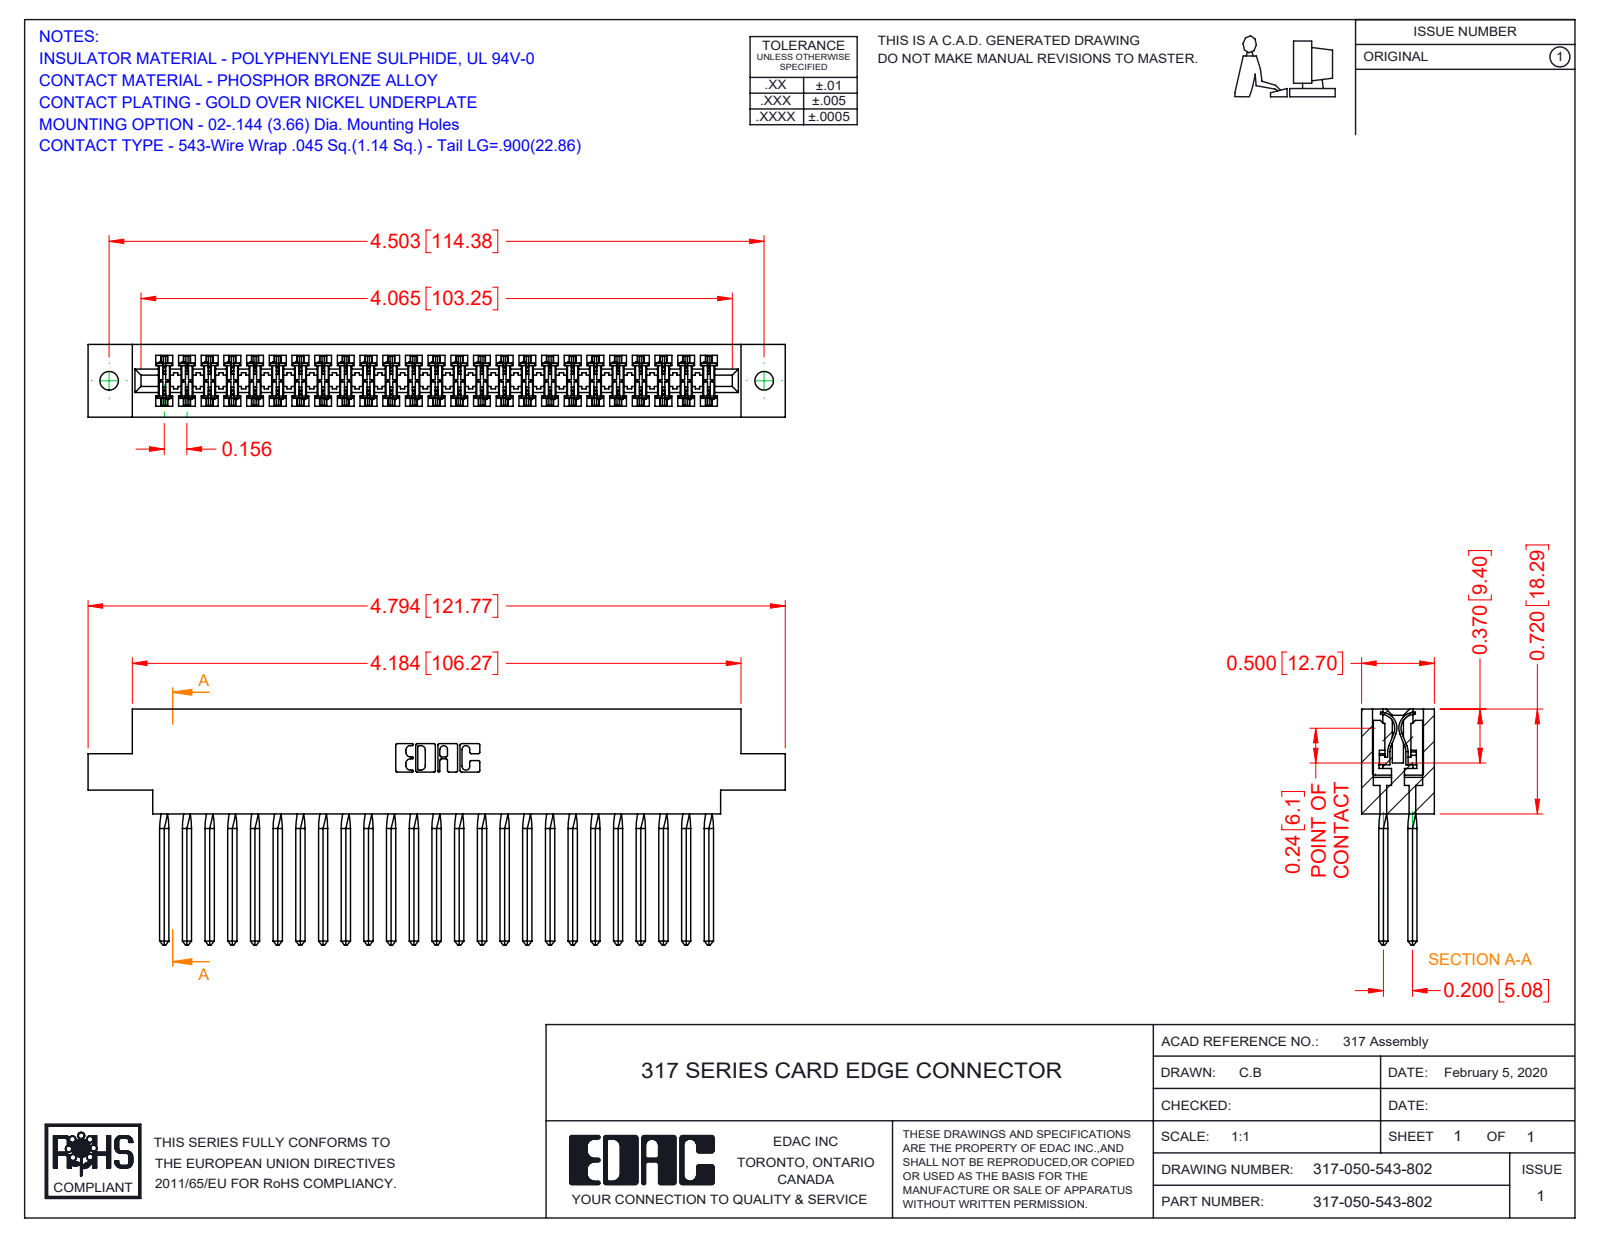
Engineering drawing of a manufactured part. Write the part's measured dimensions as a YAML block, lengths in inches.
part_name: "317-050-543-802; 317-290-001_543; 317 Part_.144 Dia"
step_written_by: "SolidWorks 2016 (CONFIG_CONTROL_DESIGN)"
units: inches
bodies: {solids: 51, faces: 4552, planar: 3708, cylindrical: 644, other: 200}
overall_size: [4.794, 1.62, 0.5]
volume: 1.225
surface_area: 45.76
round_holes:
  - {diameter: 0.128, count: 2}
partial_cylinders:
  - {radius: 0.015, count: 100}
  - {radius: 0.01, count: 22}
  - {radius: 0.007, count: 6}
  - {radius: 0.031, count: 6}
  - {radius: 0.026, count: 3}
  - {radius: 0.095, count: 2}
  - {radius: 0.1, count: 2}
  - {radius: 0.11, count: 2}
face_to_face_distances: [0.5, 0.075, 0.425, 0.11, 0.35, 0.195, 0.094, 0.72, 0.2, 0.22]
hole_center_spacings: [4.503]
